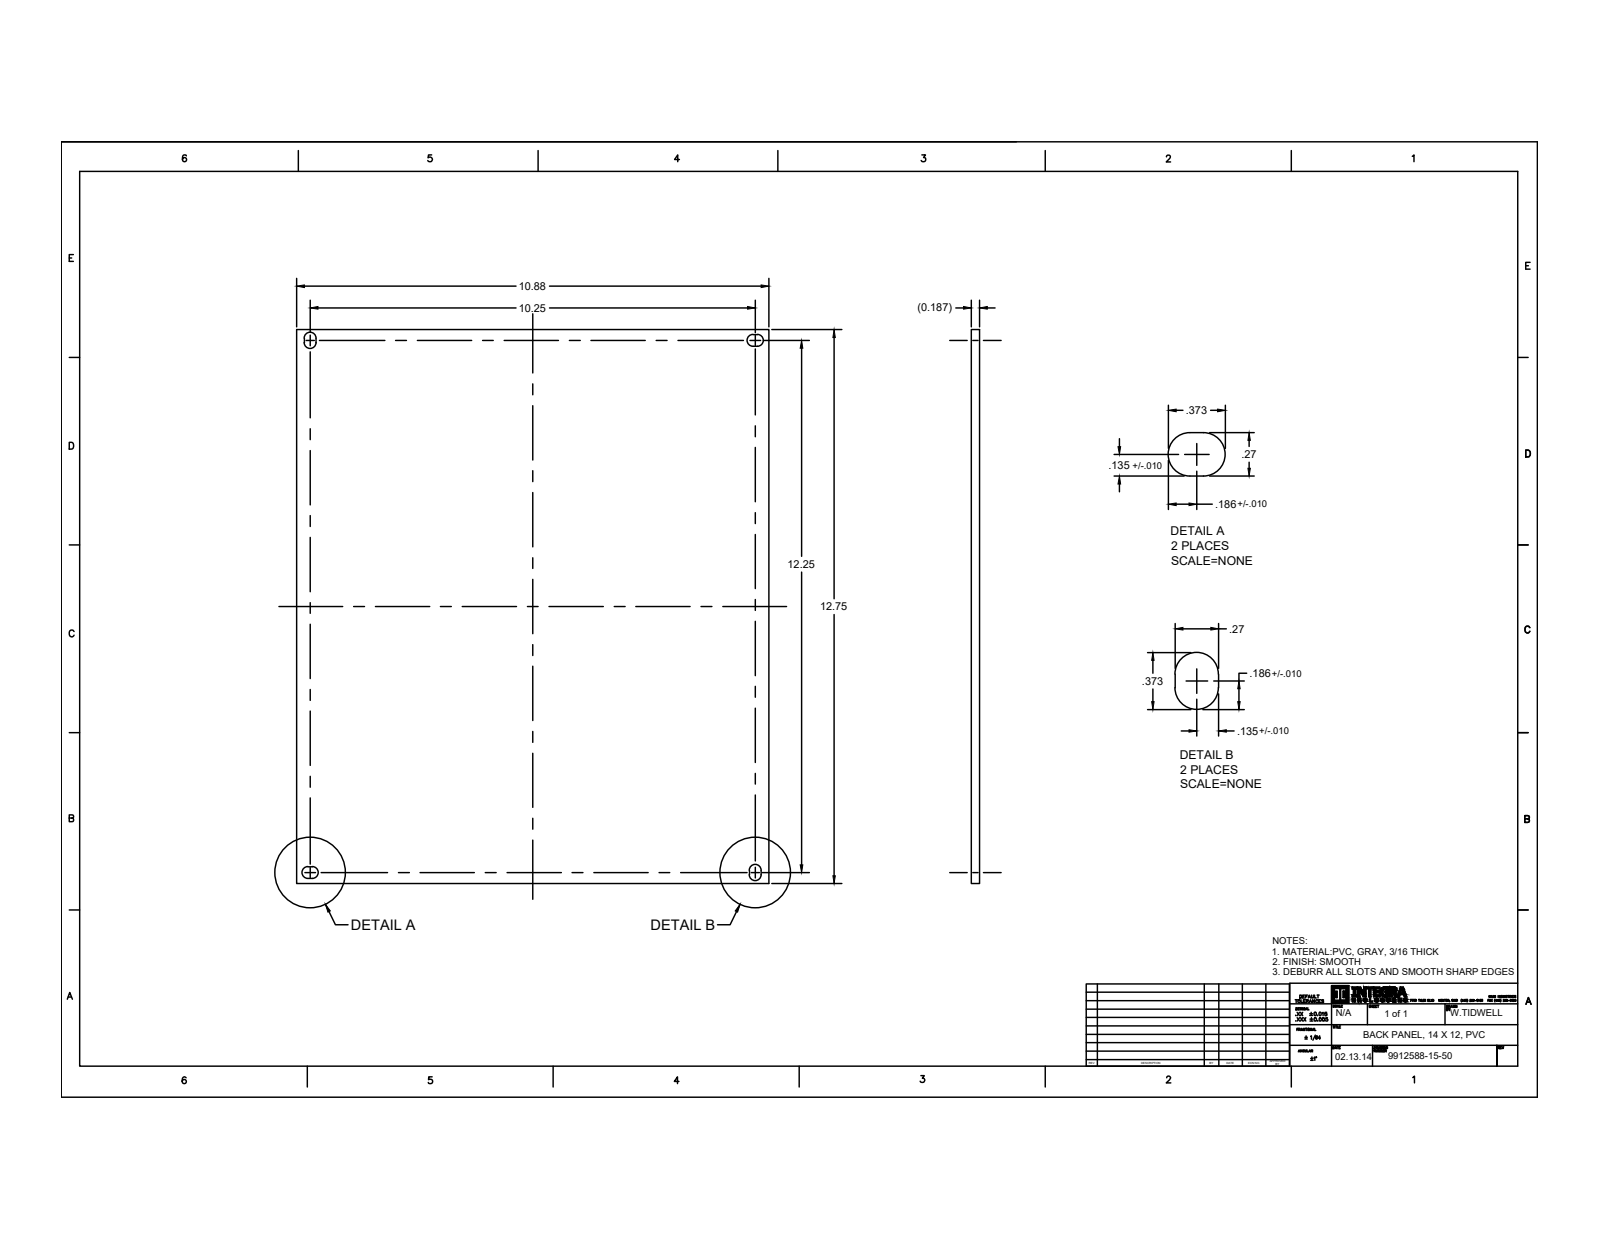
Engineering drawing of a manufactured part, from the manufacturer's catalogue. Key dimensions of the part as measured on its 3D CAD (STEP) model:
Part name (STEP PRODUCT): PVCBP-1412-P10
STEP written by: SolidWorks 2018 (AUTOMOTIVE_DESIGN)
Units: inches
Bodies: 1 solid, 22 faces (14 planar, 8 cylindrical, 0 other)
Overall size (bounding box): 12.75 × 10.88 × 0.187
Volume: 25.88 in³ · Surface area: 286.4 in²
Partial cylindrical surfaces — rounded edges, fillets, slot ends (radius × count): R0.135 ×8
Main face-to-face distances: 0.187, 10.88, 12.75, 0.27, 0.385, 12.365, 0.115, 12.635, 12.25, 0.45
